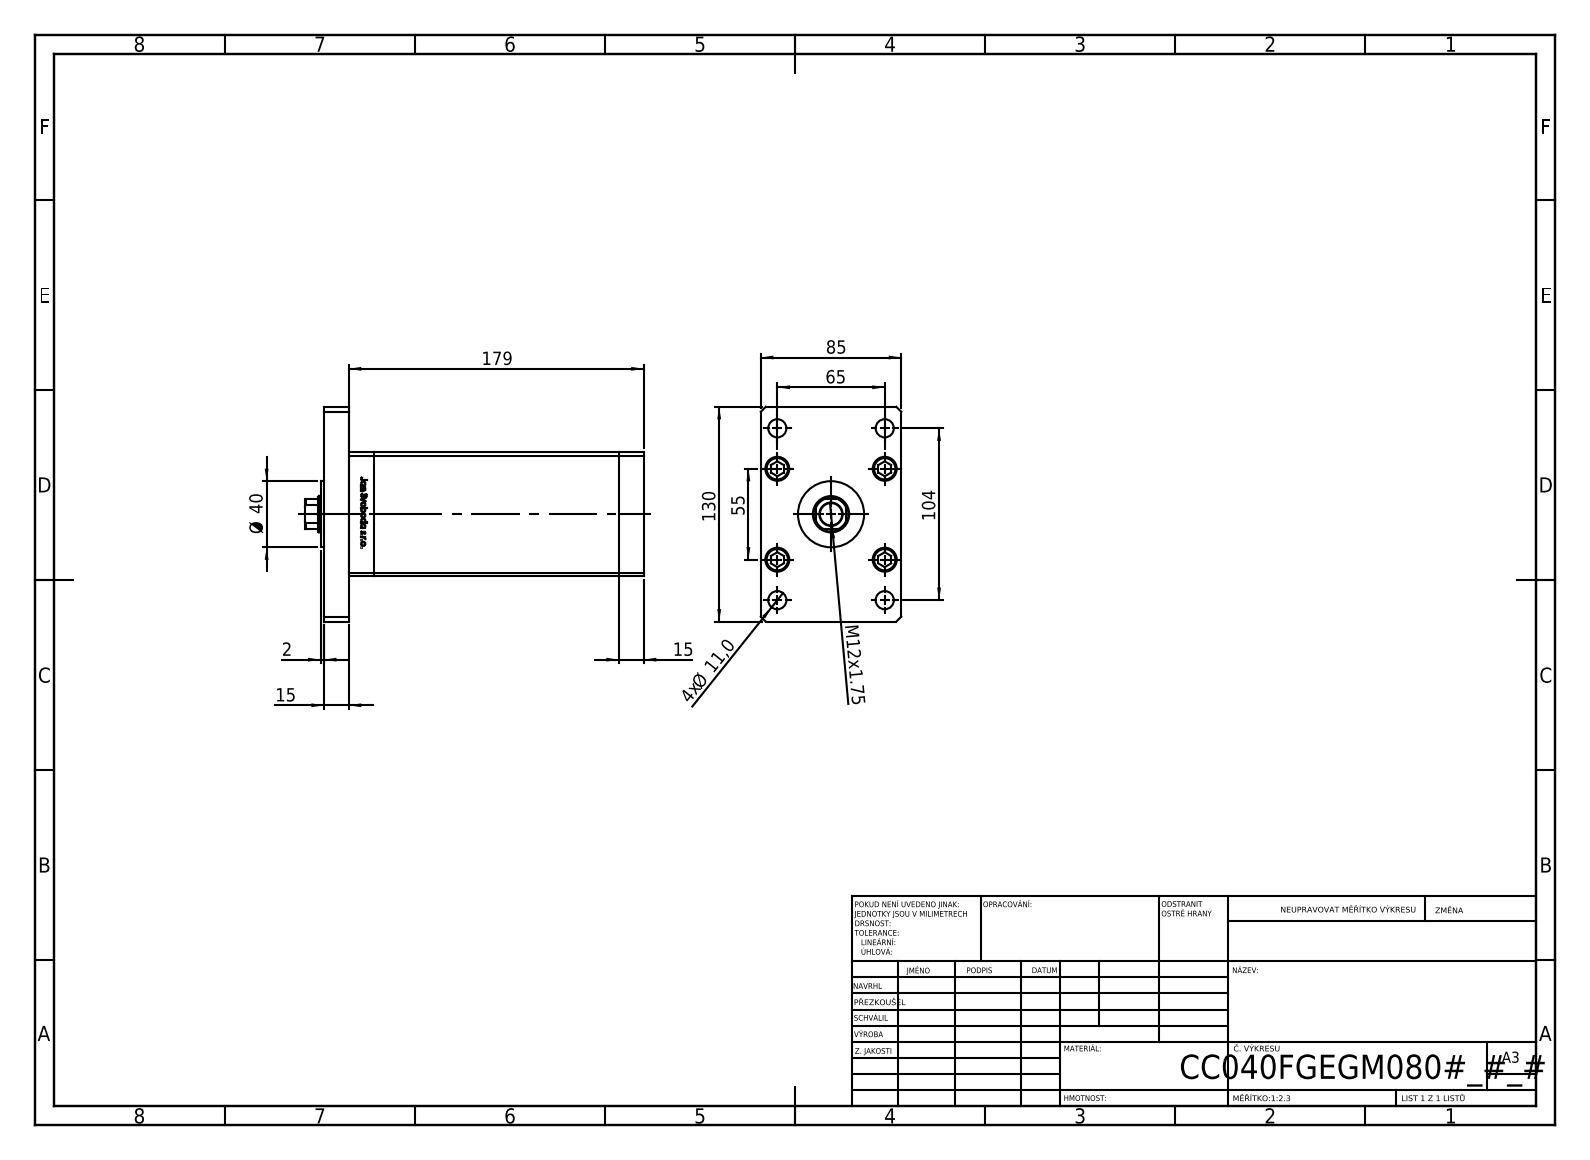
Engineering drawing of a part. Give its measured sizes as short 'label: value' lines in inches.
name: ALLEN BOLT; V220C_FRONT_F; V220C BACK_F; V220C_F_MIDDLE (+2 more)
written by: SolidWorks 2019 (CONFIG_CONTROL_DESIGN)
unit: in
bodies: 19 solids, 1310 faces (517 planar, 187 cylindrical, 606 other)
size: 8.071 × 5.118 × 3.346
volume: 71.09 in³; area: 308.3 in²
holes: 9× ⌀0.433, 5× ⌀0.61, 4× ⌀0.394, 4× ⌀0.571, 2× ⌀0.079, 2× ⌀0.518, 1× ⌀0.531, 1× ⌀0.866, 1× ⌀0.925
bosses: 9× ⌀0.315, 5× ⌀0.571, 1× ⌀1.575
rounds: 2× R0.037, 1× R0.413
face distances: 0.591, 3.346, 6.437, 7.028, 2.953, 1.181, 5.846, 7.618, 0.413, 1.083
hole spacings: 1.102, 0.965, 1.676, 2.414, 2.559, 2.735, 3.13, 4.043
